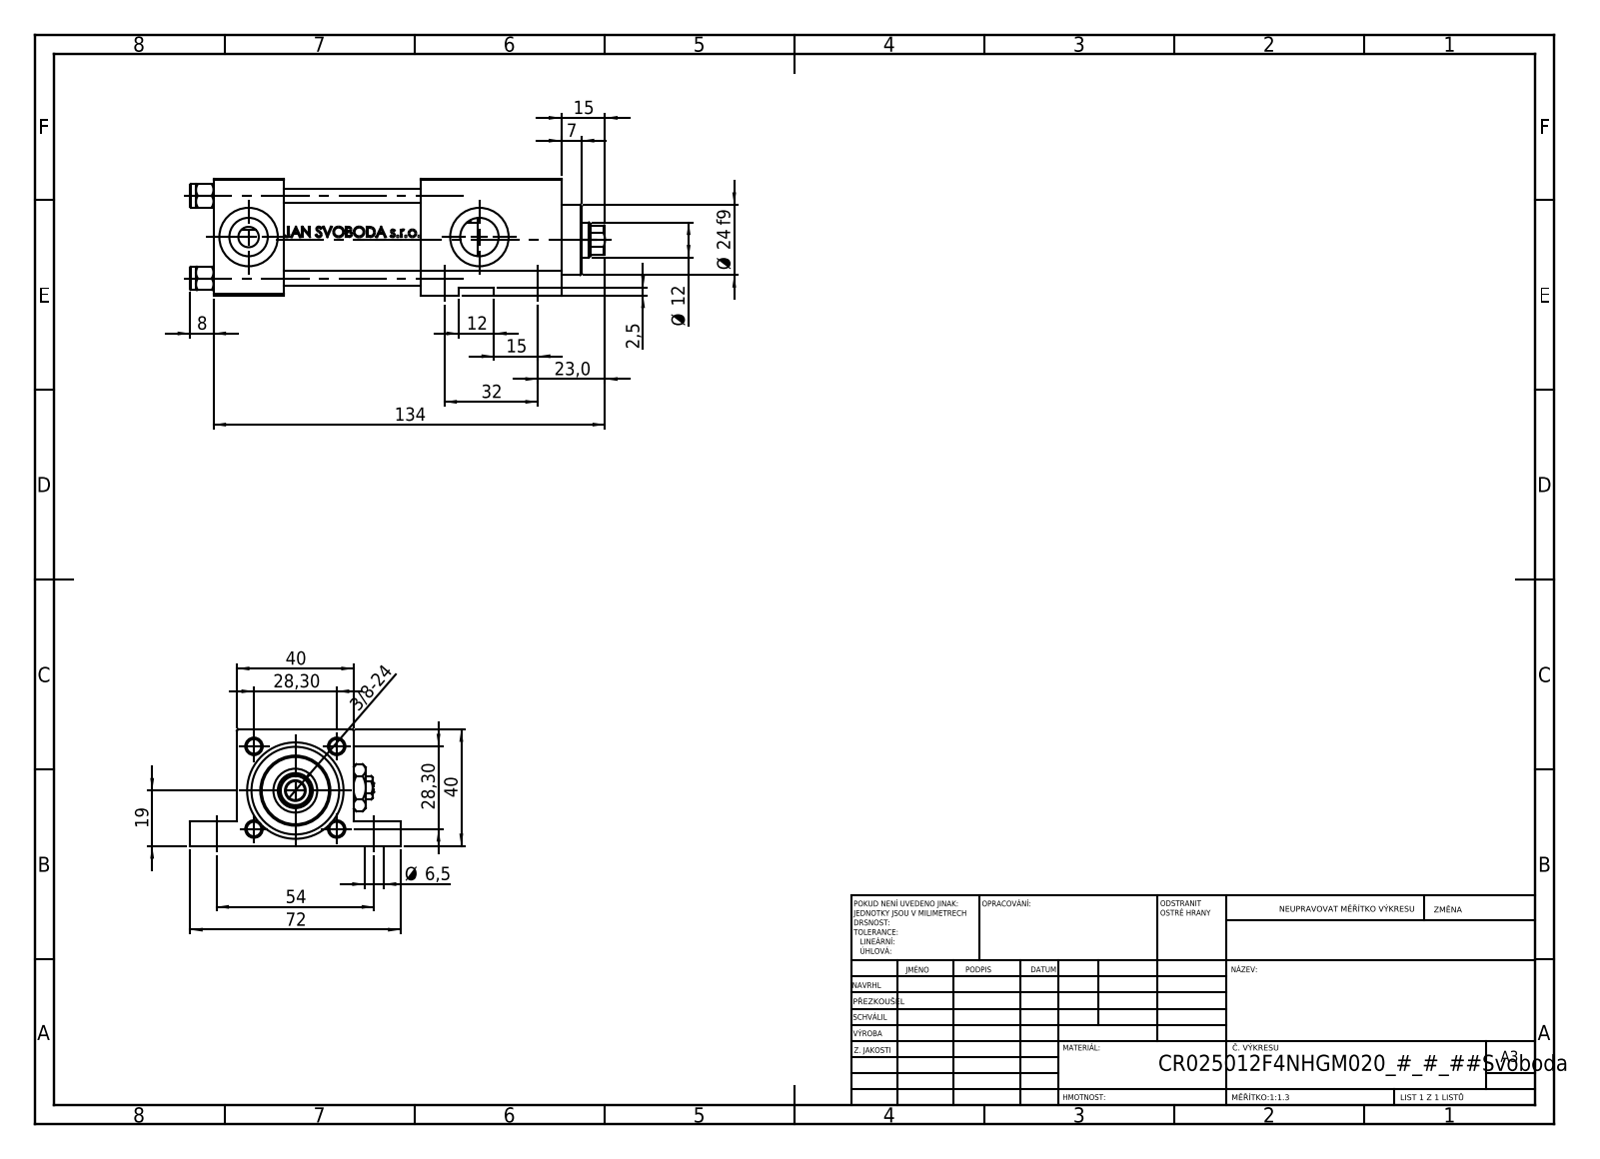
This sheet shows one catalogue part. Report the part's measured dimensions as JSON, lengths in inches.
{"part_name": "V215CR_F_Body; NUT_M5_F; V215_VC_A; Zatka_pro_OIL_PORT (+2 more)", "step_written_by": "SolidWorks 2019 (CONFIG_CONTROL_DESIGN)", "units": "inches", "bodies": {"solids": 12, "faces": 1150, "planar": 460, "cylindrical": 130, "other": 560}, "overall_size": [5.591, 2.835, 1.575], "volume_in3": 9.267, "surface_area_in2": 91.74, "round_holes": [[0.256, 5], [0.197, 4], [0.787, 4], [0.518, 3], [0.276, 2], [0.472, 1], [0.591, 1], [0.984, 1], [1.181, 1]], "round_bosses_or_shafts": [[0.315, 4], [1.22, 1], [0.945, 1]], "partial_cylinders_radius": [[0.217, 1]], "face_to_face_distances": [1.575, 0.945, 0.335, 1.24, 1.89, 1.85, 2.795, 4.685, 3.74, 0.236], "hole_center_spacings": [1.114, 0.761, 0.816, 1.26, 1.576, 2.126, 2.471, 0.276]}
